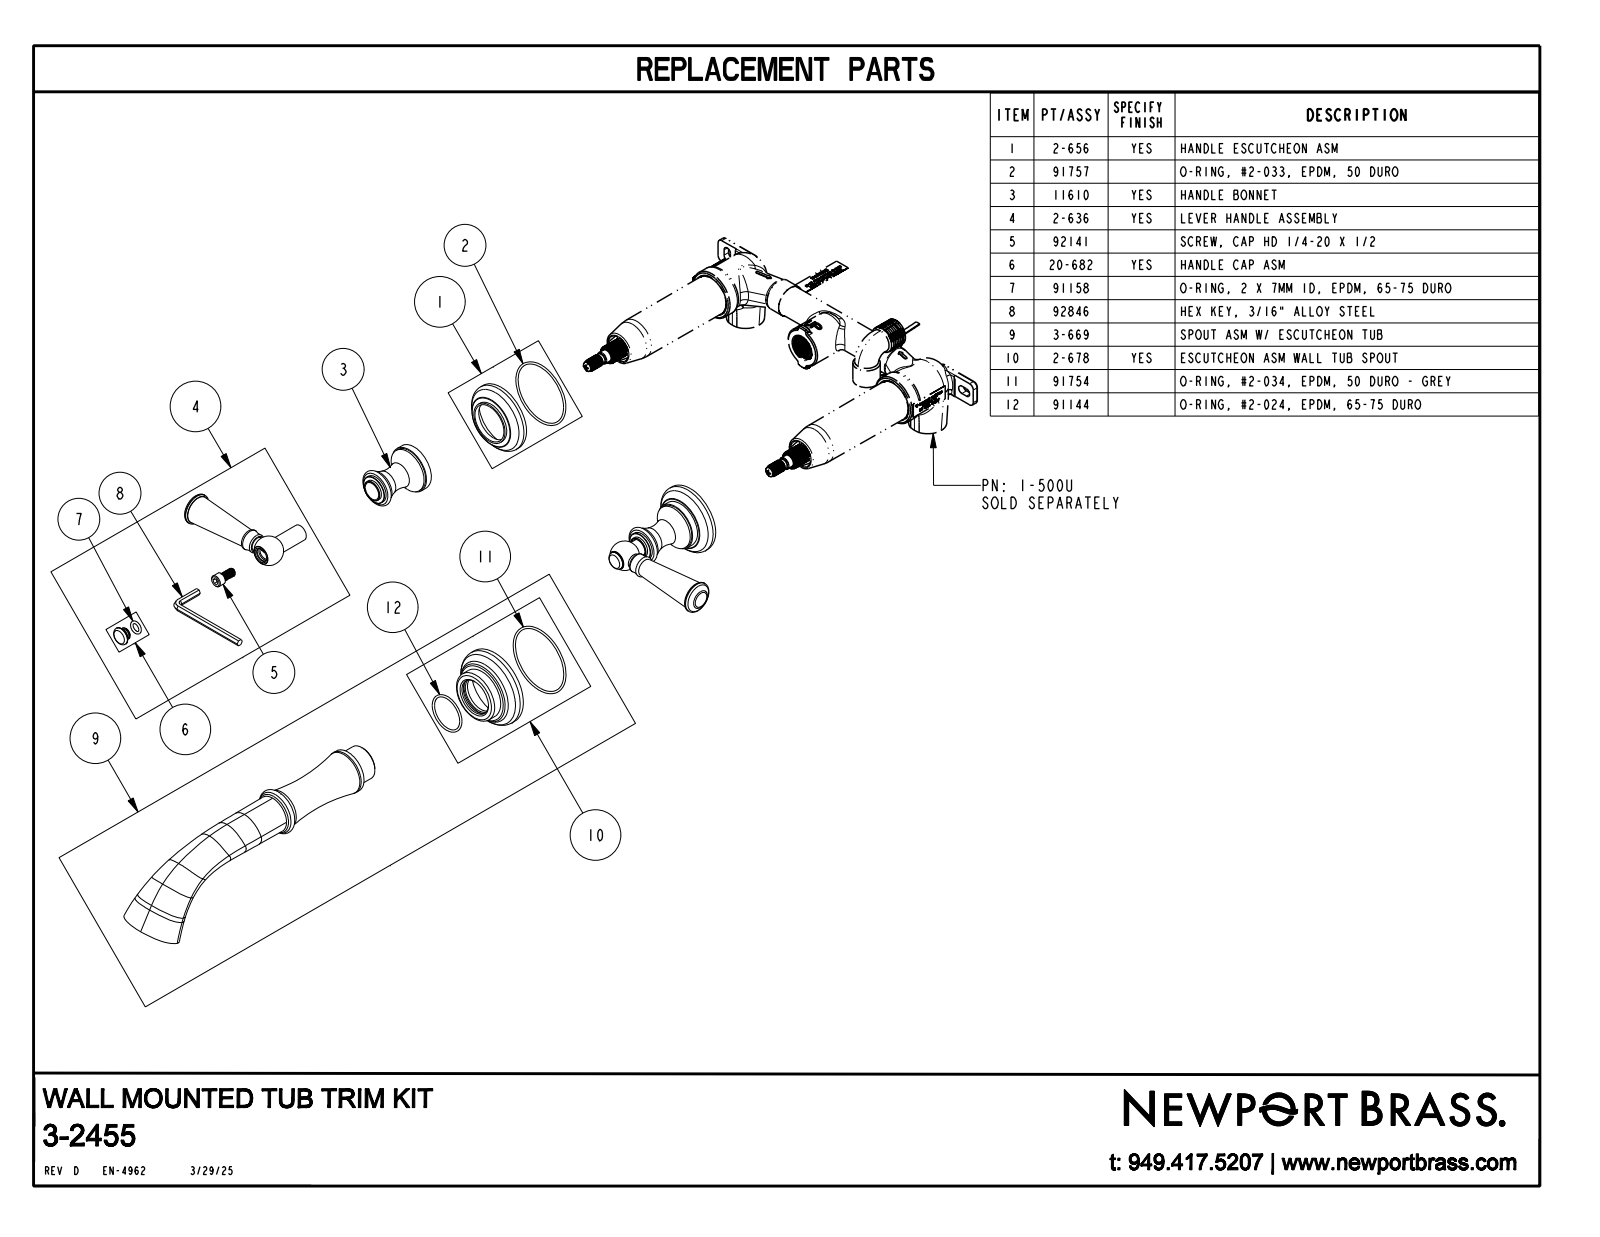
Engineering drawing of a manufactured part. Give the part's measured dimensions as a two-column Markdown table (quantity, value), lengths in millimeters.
| quantity | value |
| --- | --- |
| part name | 3-2455_SW0001 |
| STEP written by | CREO PARAMETRIC BY PTC INC, 2018400 (AUTOMOTIVE_DESIGN) |
| units | millimeters |
| bodies | 3 solids, 217 faces (29 planar, 42 cylindrical, 146 other) |
| overall size | 367.7 × 249.7 × 225.8 |
| volume | 367 600 mm³ |
| surface area | 64 050 mm² |
| round bosses / shafts (diameter × count) | 55.9 × 2, 37.8 × 2, 36.1 × 2, 22.9 × 2, 16.8 × 2, 14.2 × 2, 13.1 × 2, 63 × 1 |
| main face-to-face distances | 10.9, 2, 14, 3, 55.1, 44.2, 41.1, 53.1, 42.2, 39.1 |
